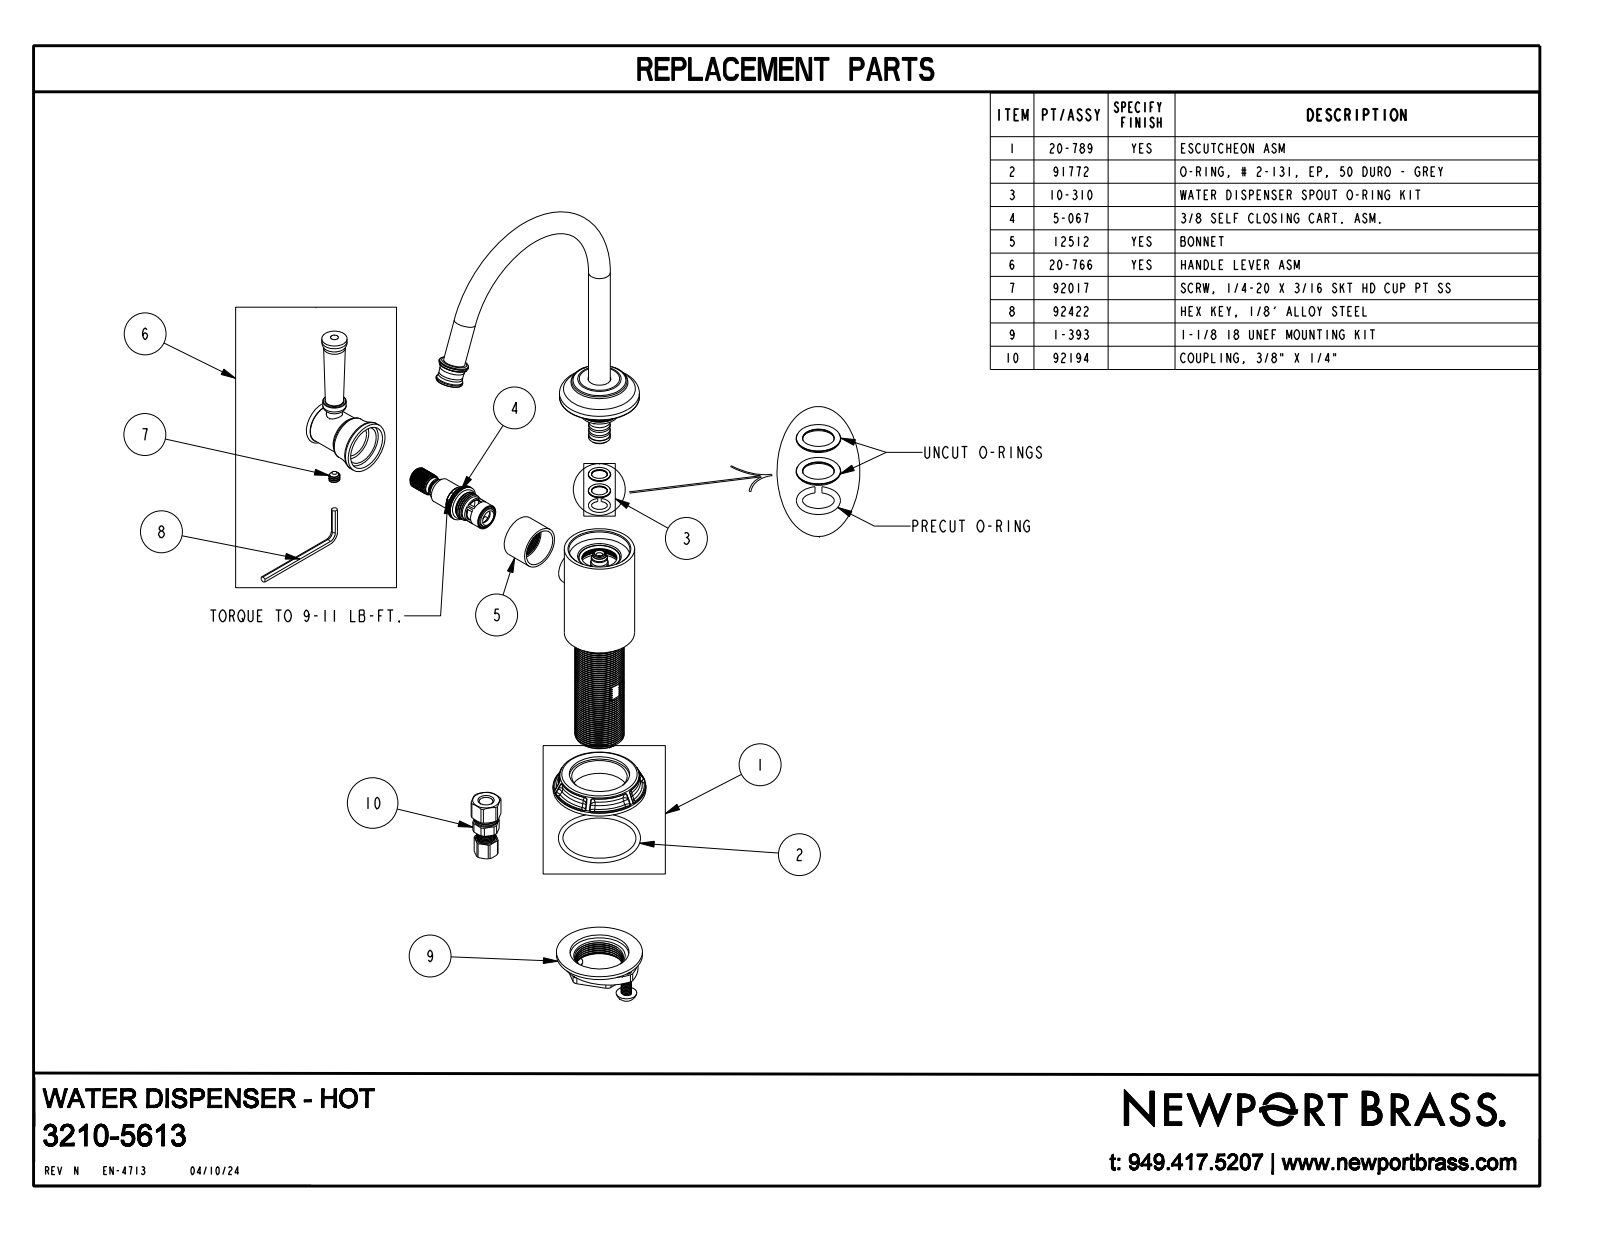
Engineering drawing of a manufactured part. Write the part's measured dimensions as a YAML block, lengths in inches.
part_name: "3210-5613"
step_written_by: "CREO PARAMETRIC BY PTC INC, 2018400 (CONFIG_CONTROL_DESIGN)"
units: inches
bodies: {solids: 1, faces: 264, planar: 20, cylindrical: 32, other: 212}
overall_size: [9.425, 6.091, 3.708]
volume: 11.29
surface_area: 53.68
round_holes:
  - {diameter: 0.375, count: 1}
  - {diameter: 1, count: 1}
round_bosses_or_shafts:
  - {diameter: 0.5, count: 2}
  - {diameter: 2.125, count: 1}
  - {diameter: 1.83, count: 1}
  - {diameter: 1.61, count: 1}
  - {diameter: 1.19, count: 1}
  - {diameter: 0.97, count: 1}
  - {diameter: 0.9, count: 1}
  - {diameter: 0.775, count: 1}
partial_cylinders:
  - {radius: 0.92, count: 1}
face_to_face_distances: [2.775, 3.306, 0.531, 1.47, 0.425, 2.35, 2.881, 0.1, 0.325, 4.541]
